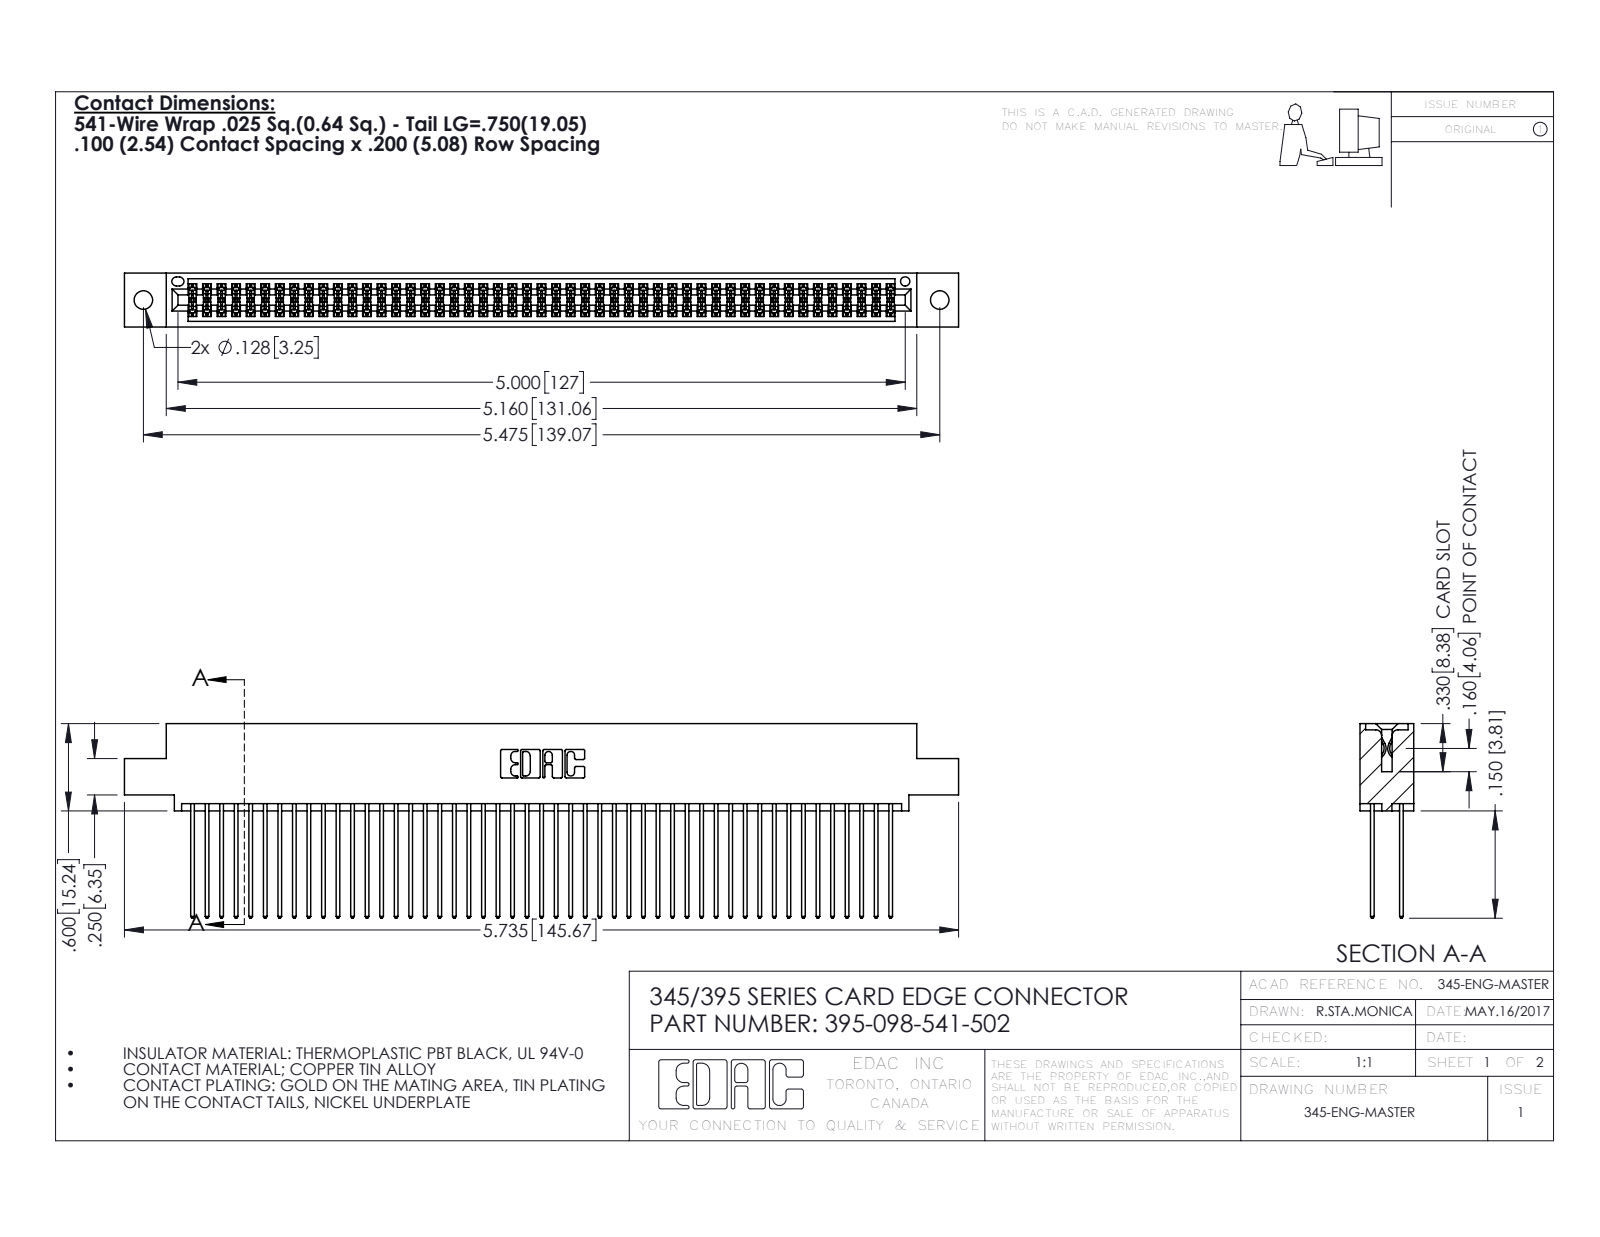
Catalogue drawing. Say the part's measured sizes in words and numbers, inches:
The part is named "395-098-541-502; 345-292-001_345-293-141; 345 Part_0.110 Offset - 0.128 Dia". Its 3-D file was written by "SolidWorks 2016 (CONFIG_CONTROL_DESIGN)". It is 99 solids with 5030 faces: 3318 planar, 1712 cylindrical and 0 other. Overall it measures 5.735 by 1.337 by 0.37 inches. Its volume is 0.895 cubic inches and its surface area 37.63 square inches. Round holes: 2 of diameter 0.128, 1 of diameter 0.064. Partial cylindrical surfaces (rounded edges, fillets, slot ends): 147 of radius 0.006, 98 of radius 0.01, 22 of radius 0.01, 6 of radius 0.007, 6 of radius 0.031, 3 of radius 0.026, 2 of radius 0.014, 2 of radius 0.019. The main face-to-face distances are 0.072, 0.298, 0.2, 0.098, 0.272, 0.025, 0.225, 0.37, 0.175, 0.149. The hole center spacings are 0.27, 5.239, 5.475.
